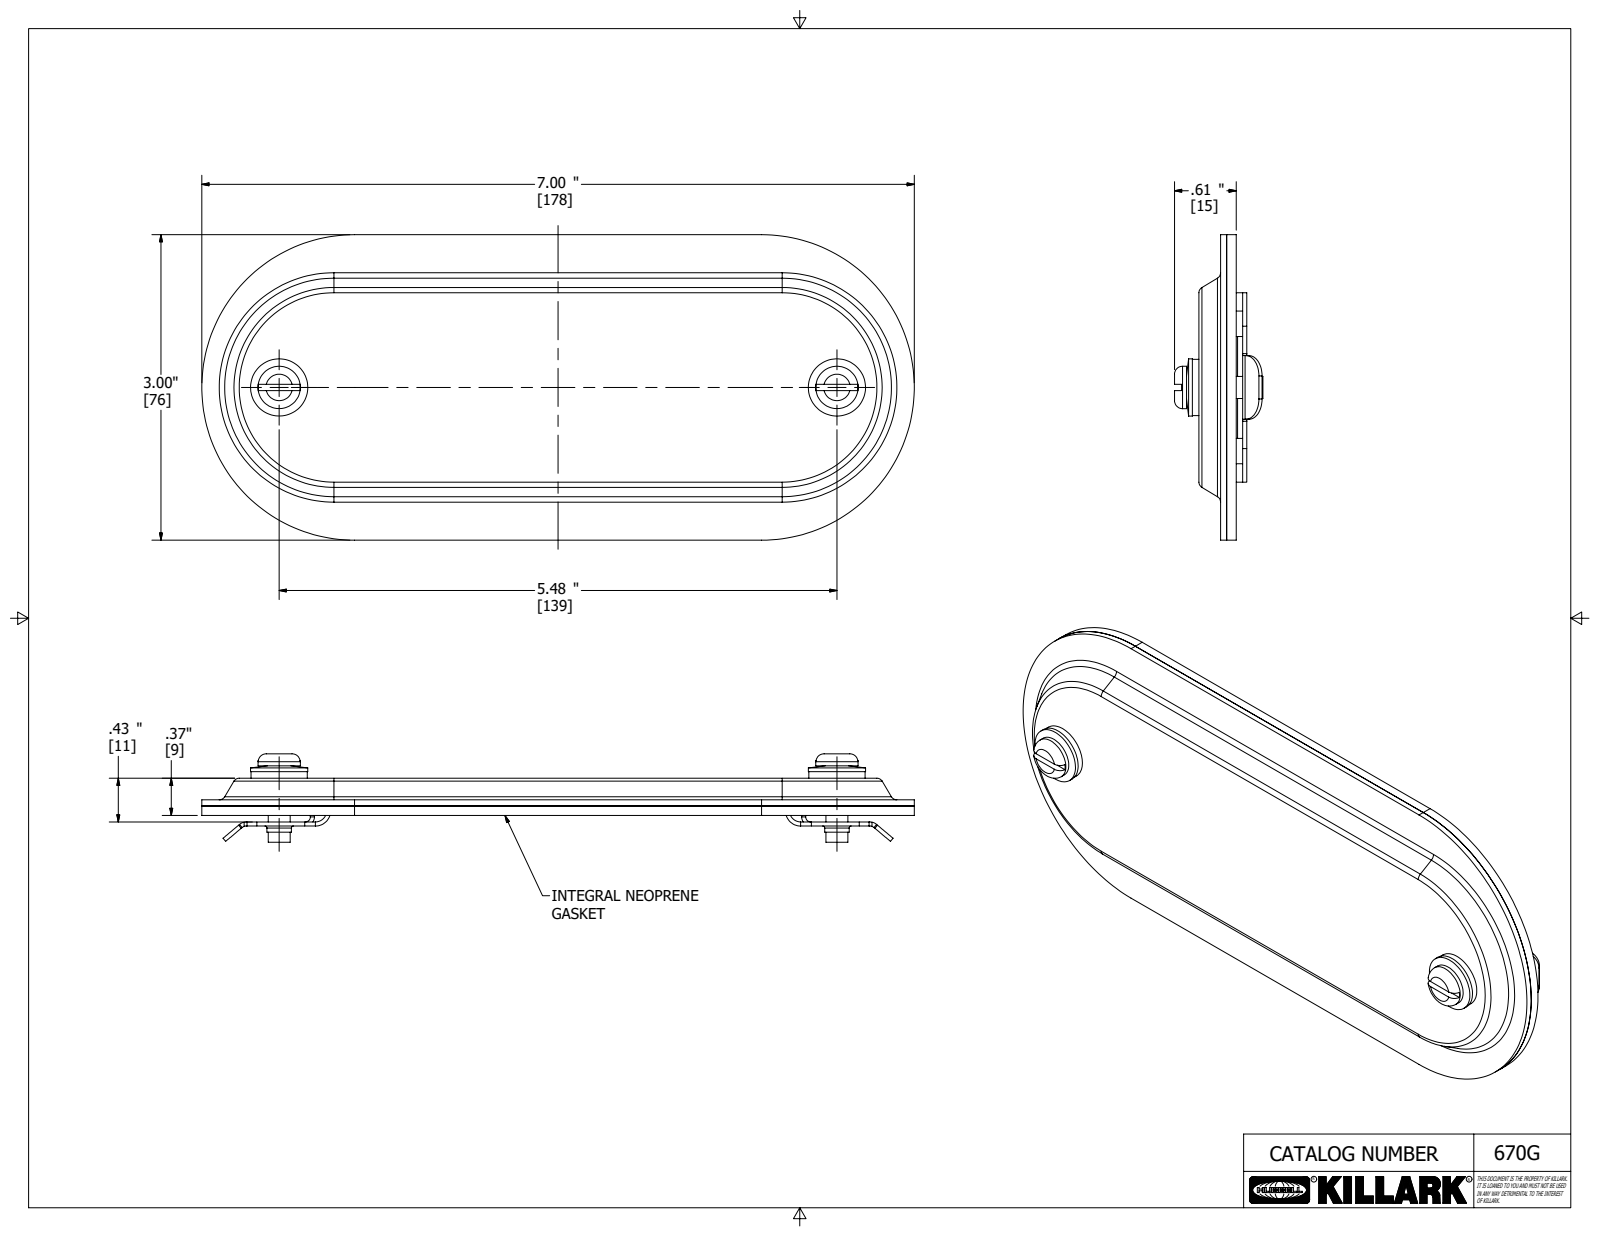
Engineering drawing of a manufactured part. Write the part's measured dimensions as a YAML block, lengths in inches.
part_name: "670G; 670; 18395; 18038FAAB (+2 more)"
step_written_by: "Autodesk Inventor 2018 (AUTOMOTIVE_DESIGN)"
units: inches
bodies: {solids: 10, faces: 246, planar: 108, cylindrical: 90, other: 48}
overall_size: [7, 3, 0.869]
volume: 2.857
surface_area: 85.84
round_holes:
  - {diameter: 0.166, count: 2}
  - {diameter: 0.2, count: 2}
  - {diameter: 0.23, count: 2}
  - {diameter: 0.242, count: 2}
round_bosses_or_shafts:
  - {diameter: 0.562, count: 2}
  - {diameter: 0.552, count: 2}
  - {diameter: 0.416, count: 2}
  - {diameter: 0.24, count: 2}
  - {diameter: 0.216, count: 2}
partial_cylinders:
  - {radius: 0.125, count: 16}
  - {radius: 0.06, count: 12}
  - {radius: 0.5, count: 6}
  - {radius: 0.03, count: 4}
  - {radius: 0.062, count: 4}
  - {radius: 0.2, count: 4}
  - {radius: 0.05, count: 2}
  - {radius: 0.09, count: 2}
face_to_face_distances: [0.094, 0.304, 0.21, 0.366, 0.272, 0.063, 0.06, 0.15, 0.154, 0.213]
hole_center_spacings: [5.48]
